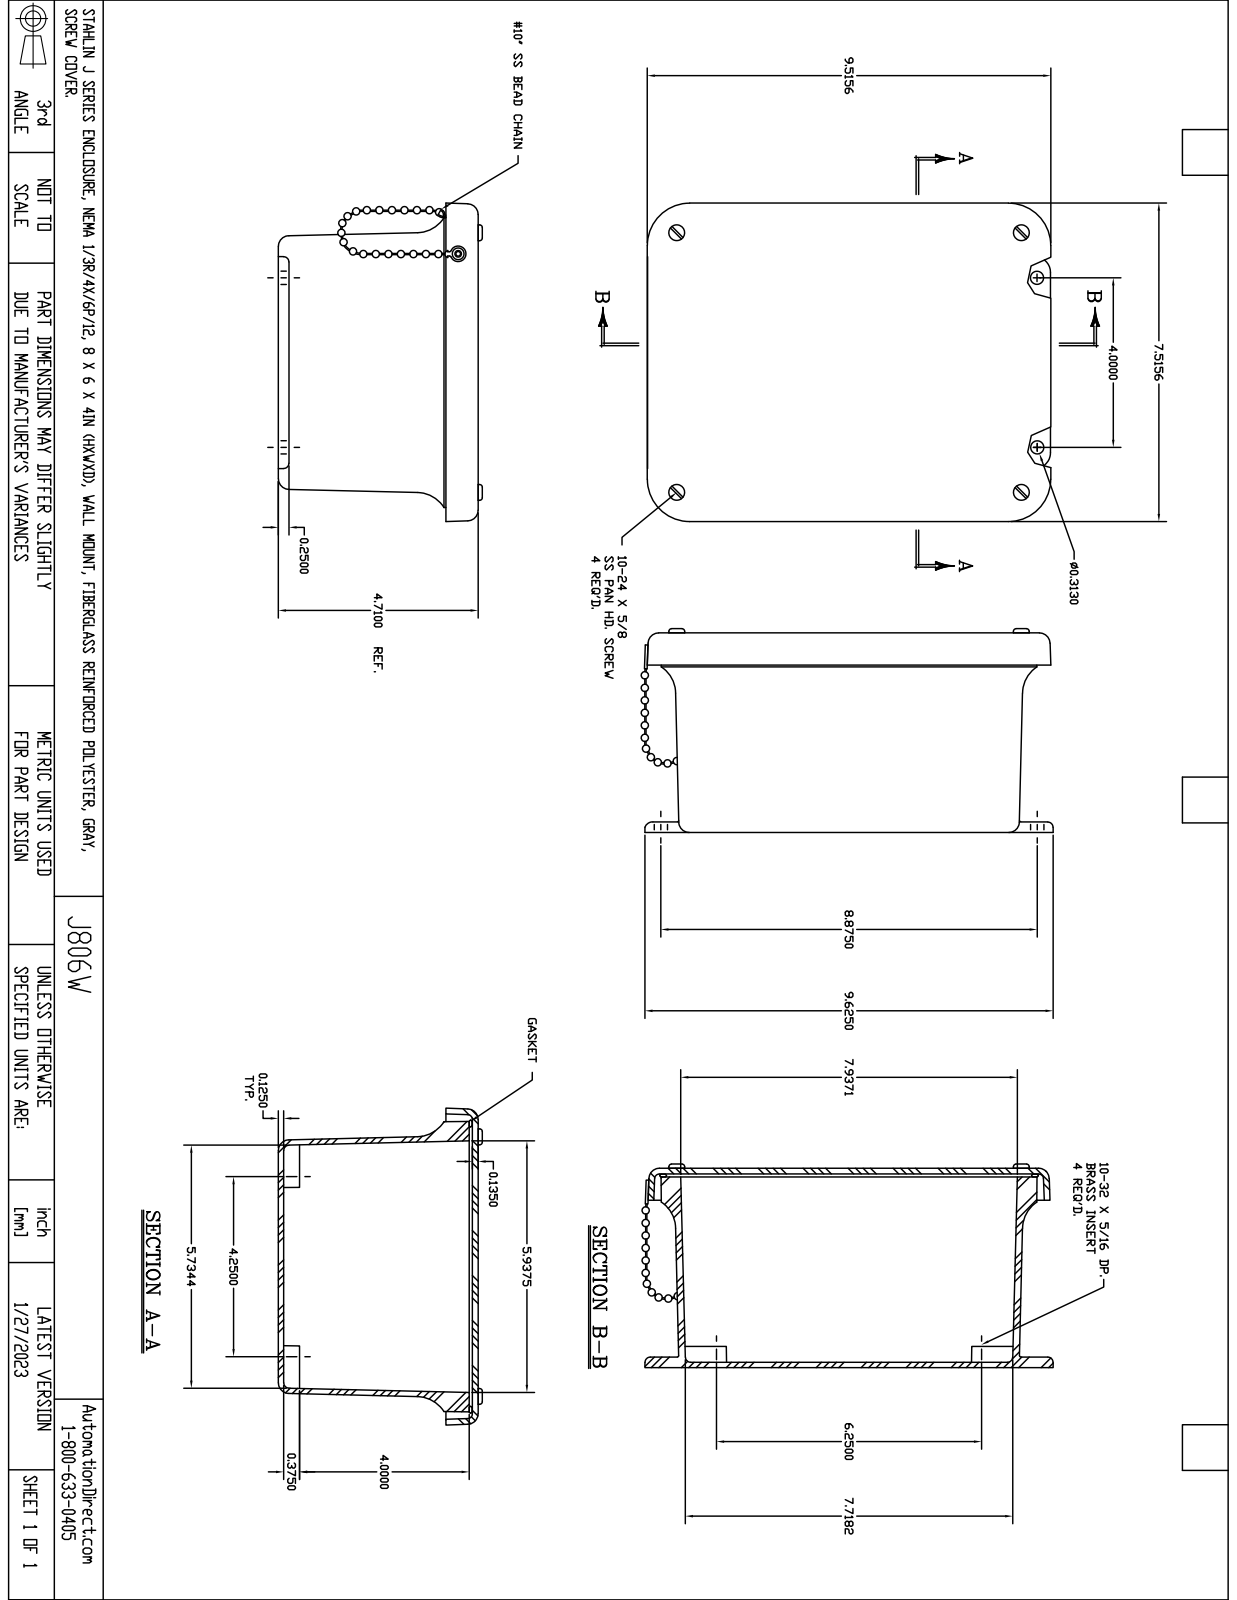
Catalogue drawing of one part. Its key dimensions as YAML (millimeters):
part_name: "M806W"
step_written_by: "SolidWorks 2018 (AUTOMOTIVE_DESIGN)"
units: millimeters
bodies: {solids: 44, faces: 777, planar: 167, cylindrical: 246, other: 364}
overall_size: [256.6, 195.3, 122.7]
volume: 733600
surface_area: 376800
round_holes:
  - {diameter: 3.9, count: 5}
  - {diameter: 3.6, count: 4}
  - {diameter: 3.7, count: 4}
  - {diameter: 4, count: 4}
  - {diameter: 5.5, count: 4}
  - {diameter: 4.7, count: 2}
  - {diameter: 3.2, count: 1}
round_bosses_or_shafts:
  - {diameter: 6.9, count: 8}
  - {diameter: 4.8, count: 3}
  - {diameter: 4, count: 3}
  - {diameter: 9.5, count: 2}
  - {diameter: 6.4, count: 2}
  - {diameter: 7.2, count: 1}
  - {diameter: 3.2, count: 1}
  - {diameter: 3.2, count: 1}
partial_cylinders:
  - {radius: 0.8, count: 20}
  - {radius: 3.2, count: 12}
  - {radius: 5.1, count: 10}
  - {radius: 6.4, count: 8}
  - {radius: 9.5, count: 4}
  - {radius: 19.5, count: 4}
  - {radius: 0.3, count: 2}
  - {radius: 0.8, count: 2}
face_to_face_distances: [3.2, 3.4, 3.2, 115.9, 119.4, 112.8, 116.2, 1.6, 114.3, 111.1]
hole_center_spacings: [33.7, 133.9, 184.1, 225.1, 108, 155.6, 158.8, 192]
